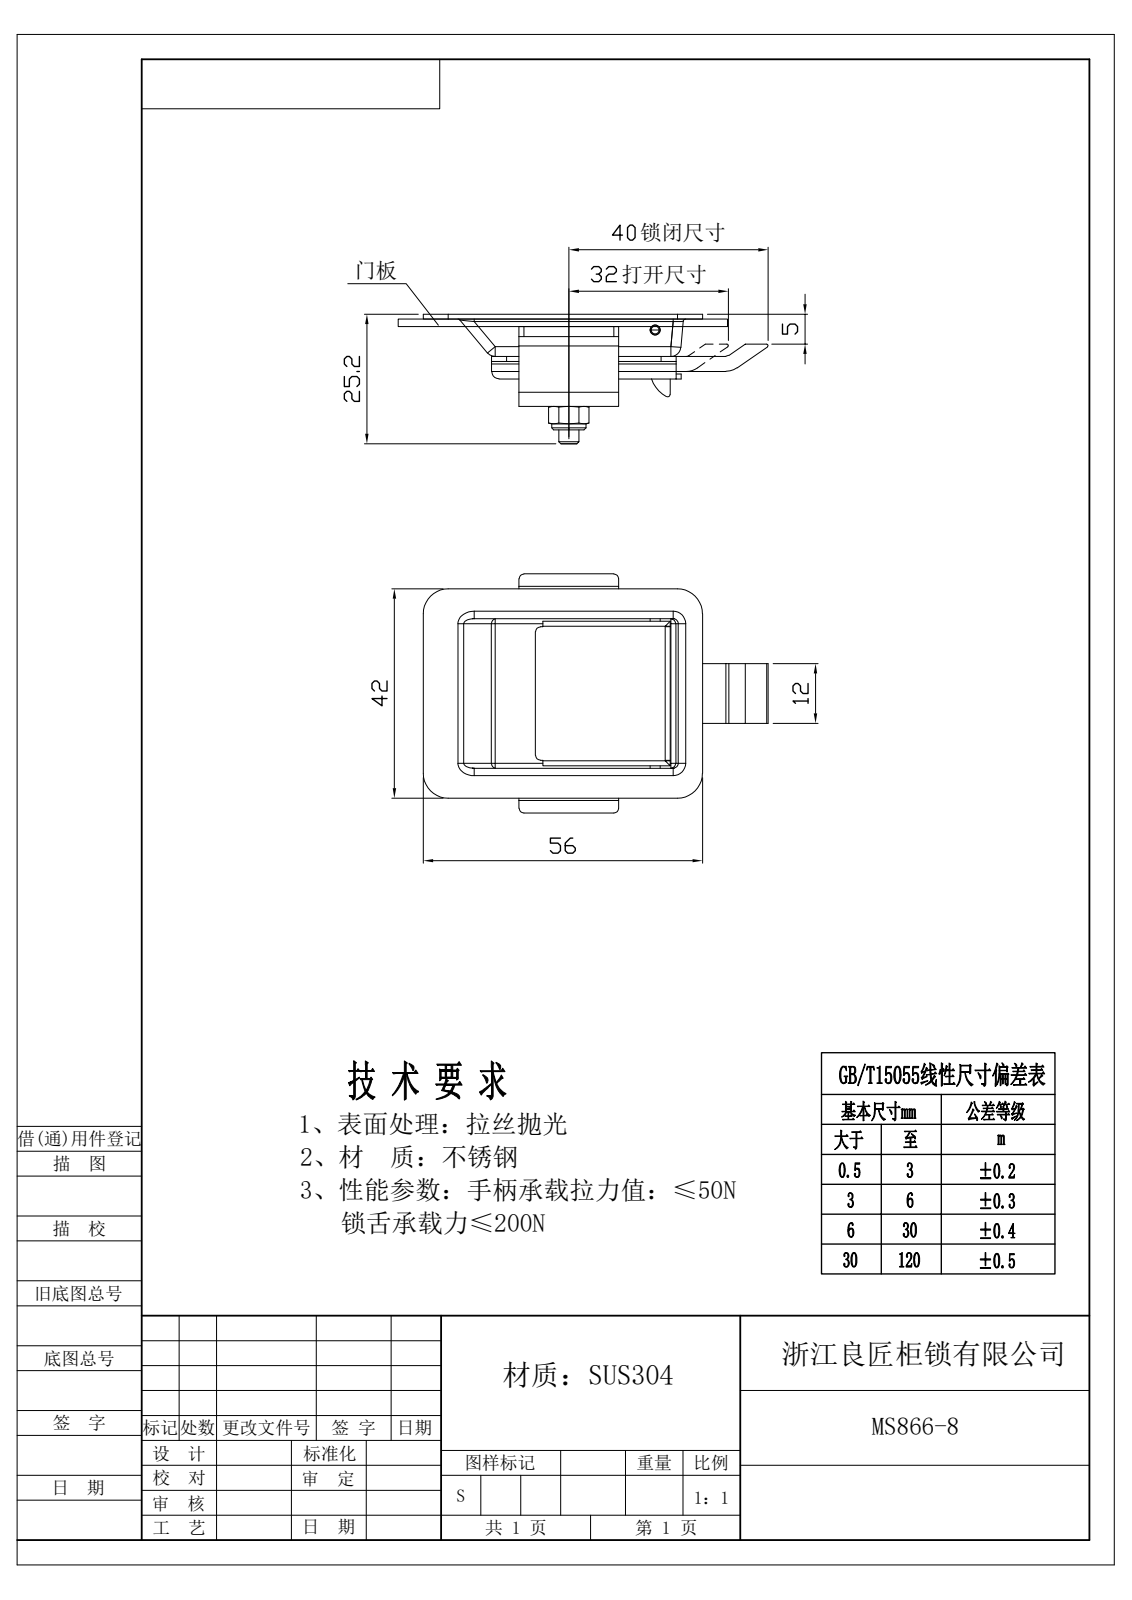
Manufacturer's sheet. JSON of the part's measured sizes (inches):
{"step_written_by": "Rhino 8.5 (CONFIG_CONTROL_DESIGN)", "units": "inches", "bodies": {"solids": 7, "faces": 383, "planar": 207, "cylindrical": 119, "other": 57}, "overall_size": [2.723, 1.89, 1.024], "volume_in3": 0.515, "surface_area_in2": 26.14, "round_holes": [[0.079, 4], [0.063, 1], [0.083, 1], [0.118, 1], [0.126, 1], [0.177, 1]], "round_bosses_or_shafts": [[0.271, 1], [0.157, 1], [0.118, 1], [0.079, 1]], "partial_cylinders_radius": [[0.039, 24], [0.02, 18], [0.059, 10], [0.079, 10], [0.118, 6], [0.197, 4], [0.157, 3], [0.012, 1]], "face_to_face_distances": [0.039, 0.295, 0.177, 0.256, 0.335, 0.079, 0.138, 0.217, 0.472, 0.433], "hole_center_spacings": [0.528, 0.625, 0.63, 0.837, 1.055, 1.1, 1.229, 0.315]}
